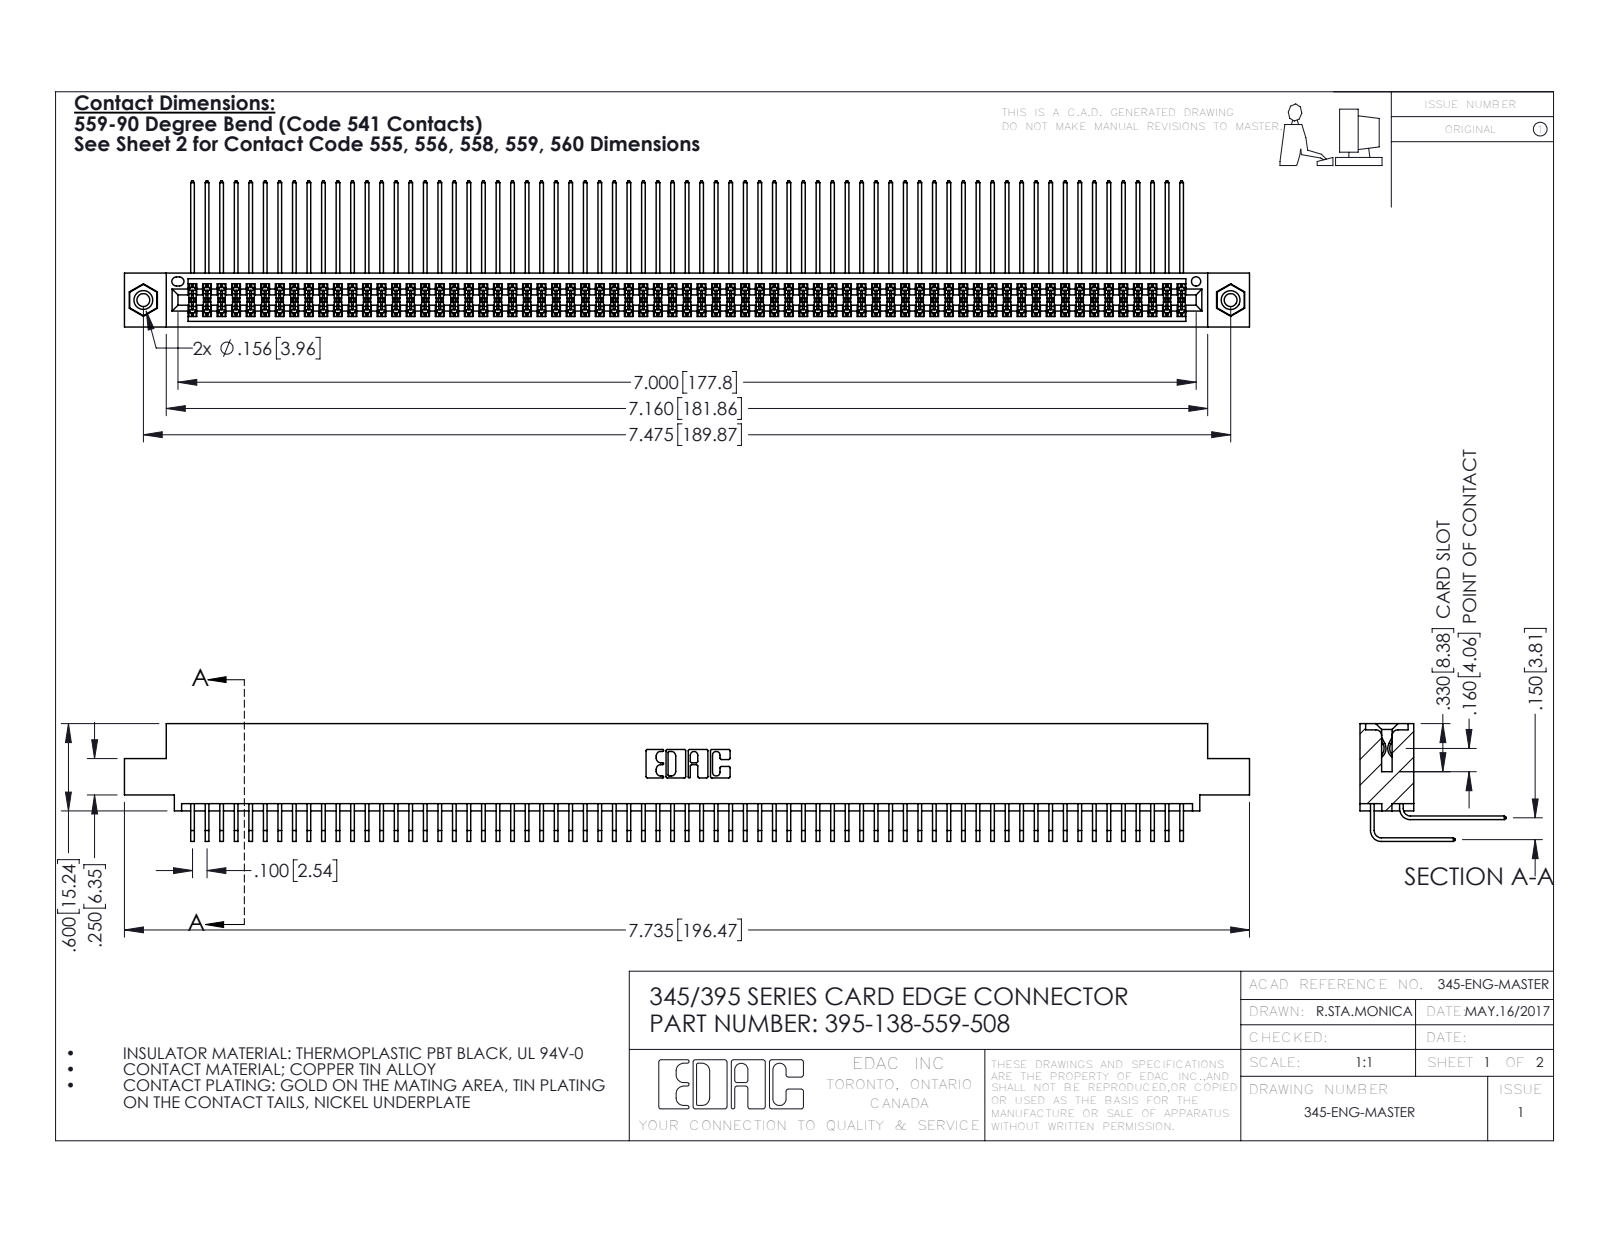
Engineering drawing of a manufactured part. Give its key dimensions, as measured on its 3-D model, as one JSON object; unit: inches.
{"part_name": "345 Part_0.110 Offset - 0.156 Dia-TI; 345-250-001_345-250-003-102; 395-138-559-508; 345-292-001_558 559 Tail - 1 (+1 more)", "step_written_by": "SolidWorks 2016 (CONFIG_CONTROL_DESIGN)", "units": "inches", "bodies": {"solids": 141, "faces": 7366, "planar": 4946, "cylindrical": 2404, "other": 16}, "overall_size": [7.735, 1.005, 0.809], "volume_in3": 1.224, "surface_area_in2": 52.72, "round_holes": [[0.089, 2], [0.125, 2], [0.156, 2], [0.064, 1]], "round_bosses_or_shafts": [[0.155, 2]], "partial_cylinders_radius": [[0.006, 275], [0.01, 22], [0.007, 6], [0.031, 6], [0.026, 3], [0.014, 2], [0.019, 2], [0.022, 2]], "face_to_face_distances": [0.072, 0.298, 0.2, 0.37, 0.098, 0.272, 0.025, 0.225, 0.175, 0.15], "hole_center_spacings": [0.27, 7.239, 7.475]}
